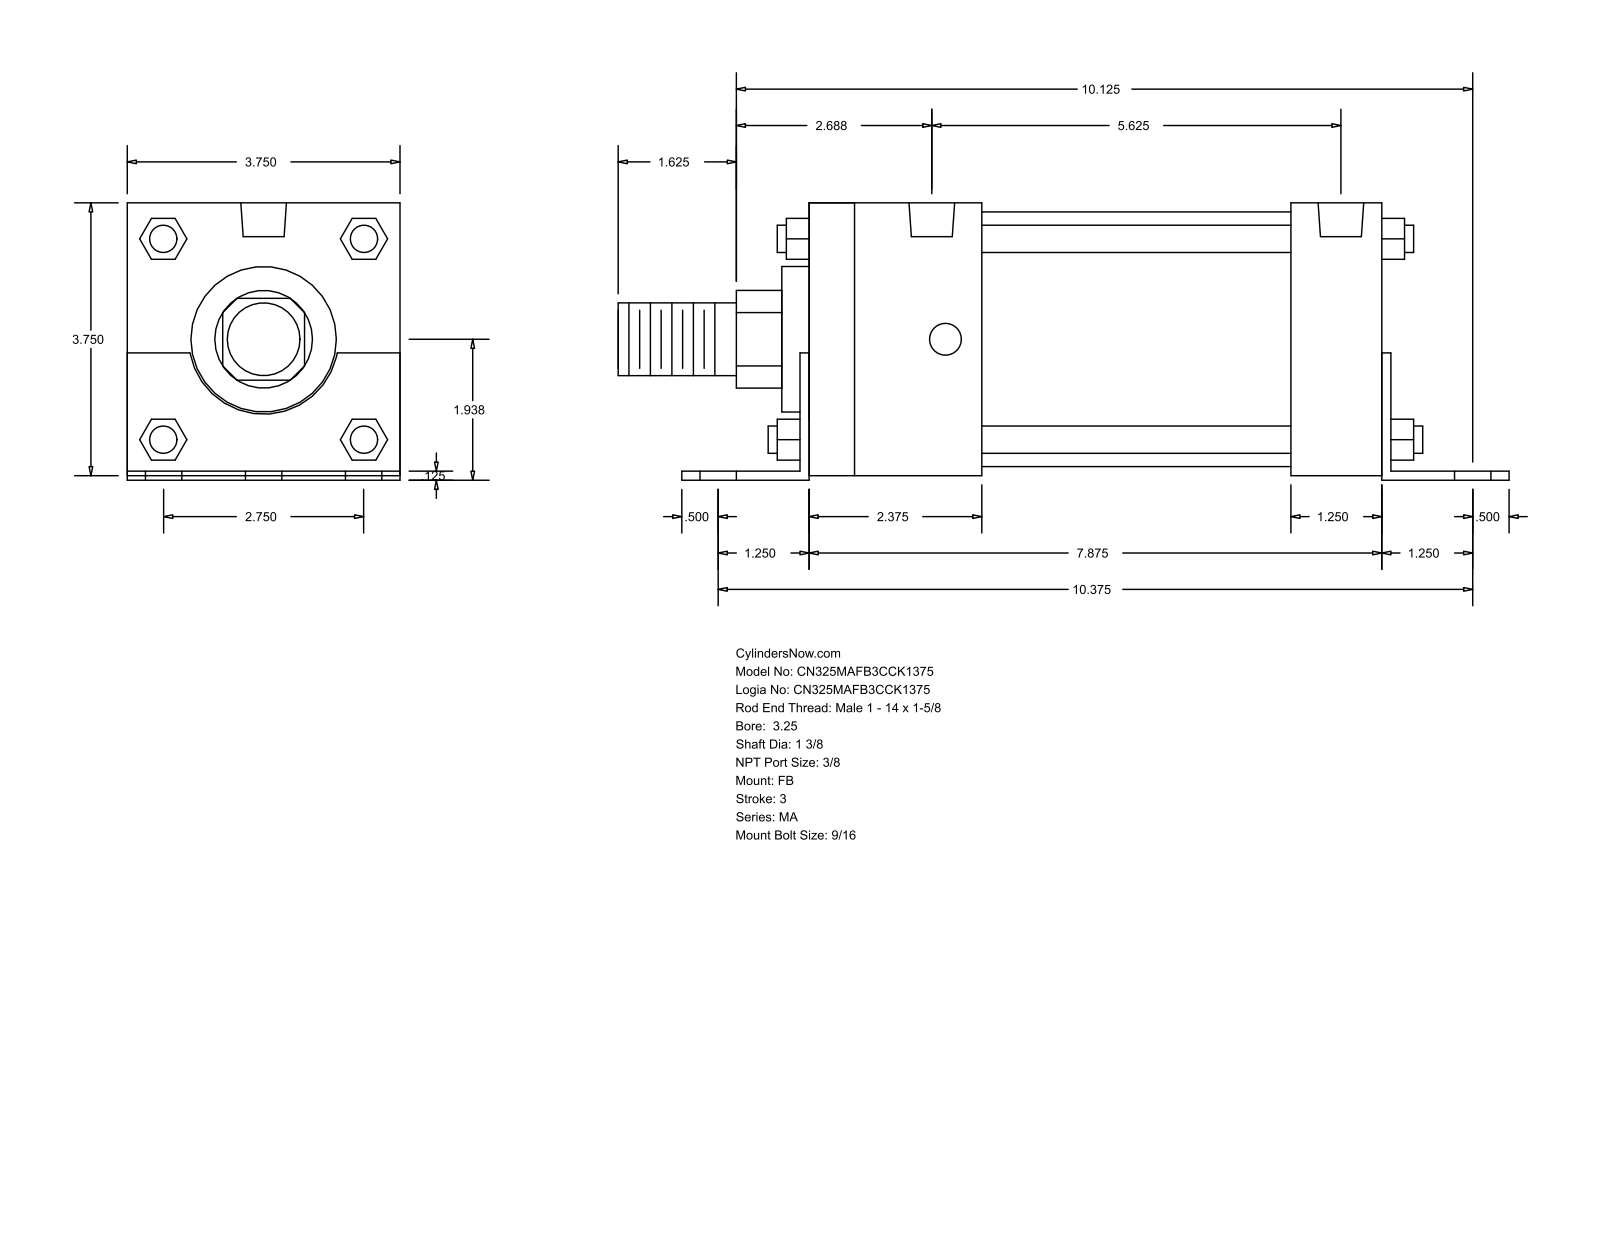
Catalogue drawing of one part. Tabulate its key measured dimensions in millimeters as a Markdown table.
| quantity | value |
| --- | --- |
| part name | MA_FB__0325_1.375 |
| STEP written by | GSSL Pune (CONFIG_CONTROL_DESIGN) |
| units | millimeters |
| bodies | 0 solids, 140 faces (105 planar, 35 cylindrical, 0 other) |
| overall size | 311.15 × 96.84 × 95.25 |
| round holes (diameter × count) | 14.29 × 6, 11.11 × 4, 15.93 × 2 |
| round bosses / shafts (diameter × count) | 9.53 × 4, 88.9 × 1, 50.8 × 1, 34.92 × 1, 25.4 × 1 |
| partial cylindrical surfaces (radius × count) | 17.06 × 1, 26.16 × 1 |
| main face-to-face distances | 95.24, 3.17, 1.59, 96.83, 1.58, 93.66, 203.2, 200.03, 31.75, 34.92 |
| hole center spacings | 34.92, 265.83, 263.53, 57.78, 61.64, 69.84, 82.38, 86.72 |
